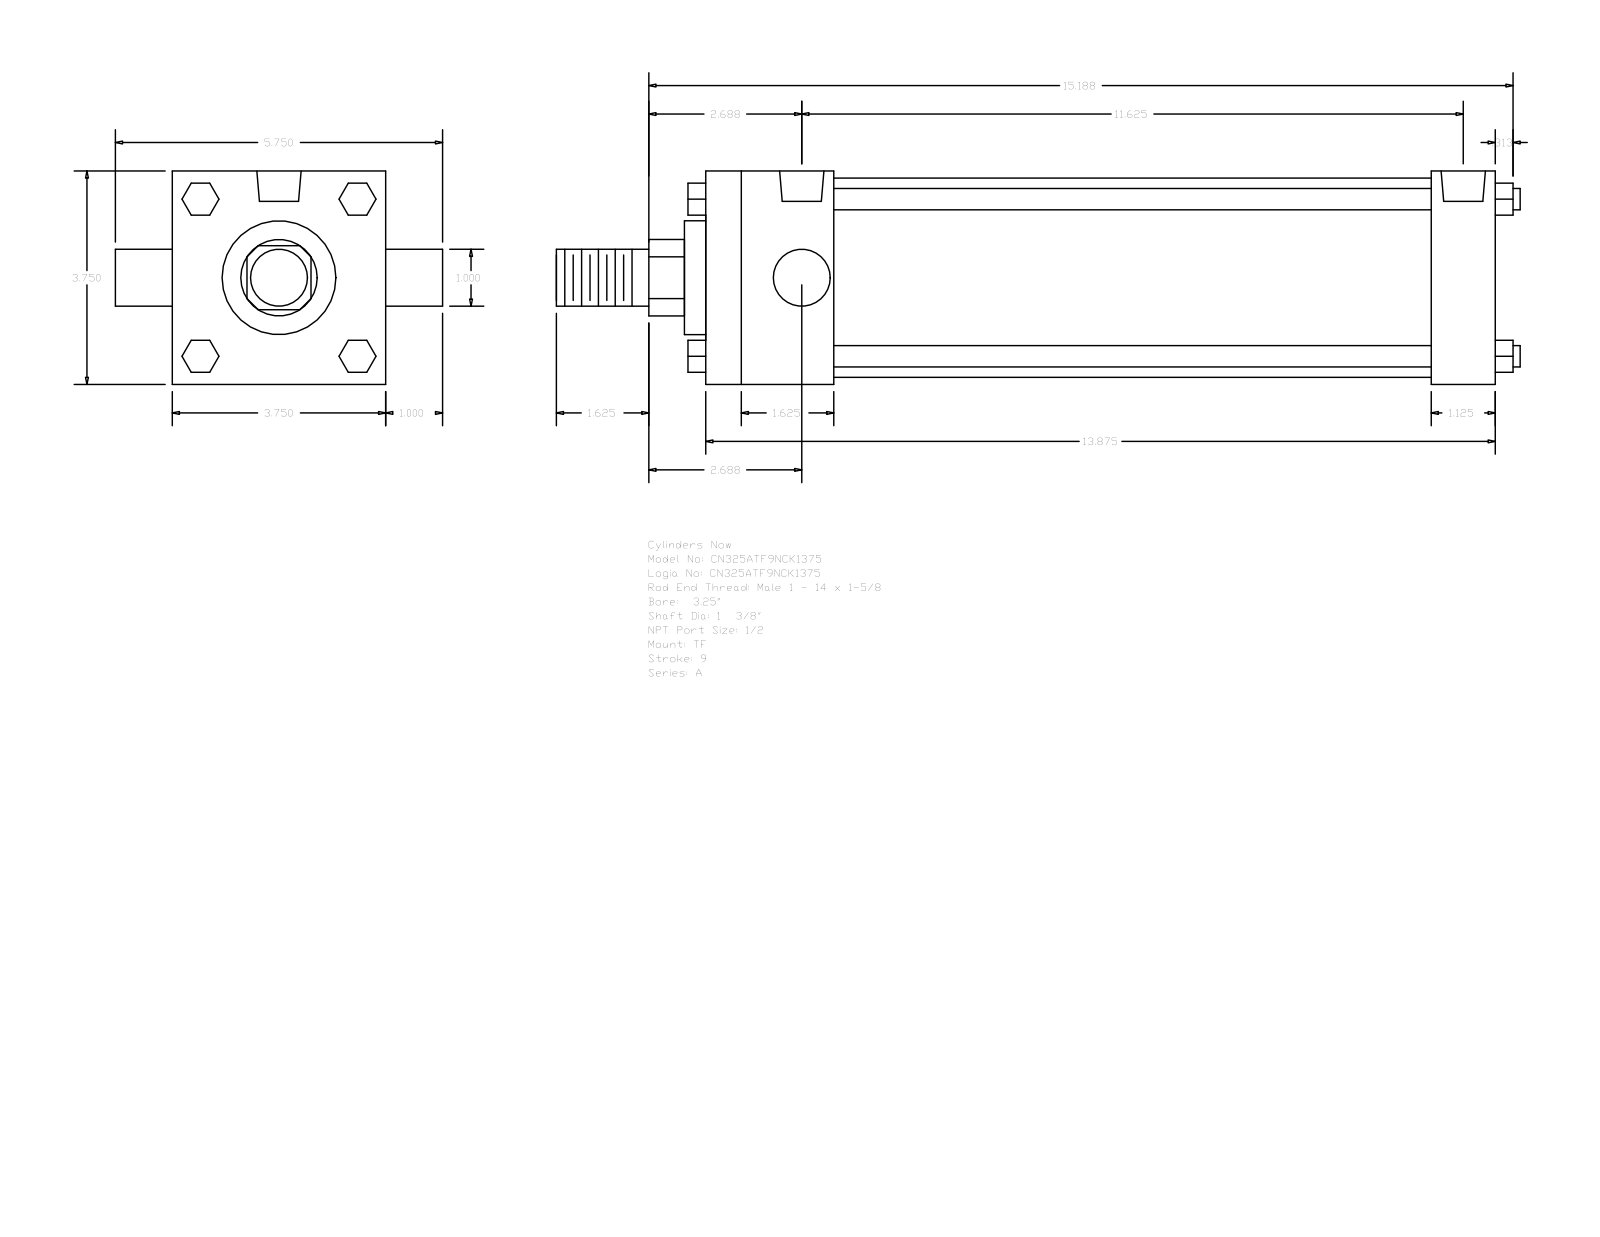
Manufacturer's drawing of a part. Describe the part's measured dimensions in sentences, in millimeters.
The part is named "A_TF__0325_1.375". Its 3-D file was written by "GSSL Pune (CONFIG_CONTROL_DESIGN)". It is 0 solids with 120 faces: 92 planar, 28 cylindrical and 0 other. Overall it measures 430.21 by 146.05 by 95.25 millimeters. Round holes: 3 of diameter 8.73, 2 of diameter 19.77. Round bosses or shafts: 4 of diameter 9.53, 2 of diameter 25.4, 1 of diameter 88.9, 1 of diameter 50.8, 1 of diameter 34.92. Partial cylindrical surfaces (rounded edges, fillets, slot ends): 1 of radius 17.06. The main face-to-face distances are 95.24, 352.42, 57.15, 323.85, 266.7, 295.27, 28.57, 66.67, 9.52, 333.37. The hole center spacings are 3.18, 292.1, 288.92, 295.28.
